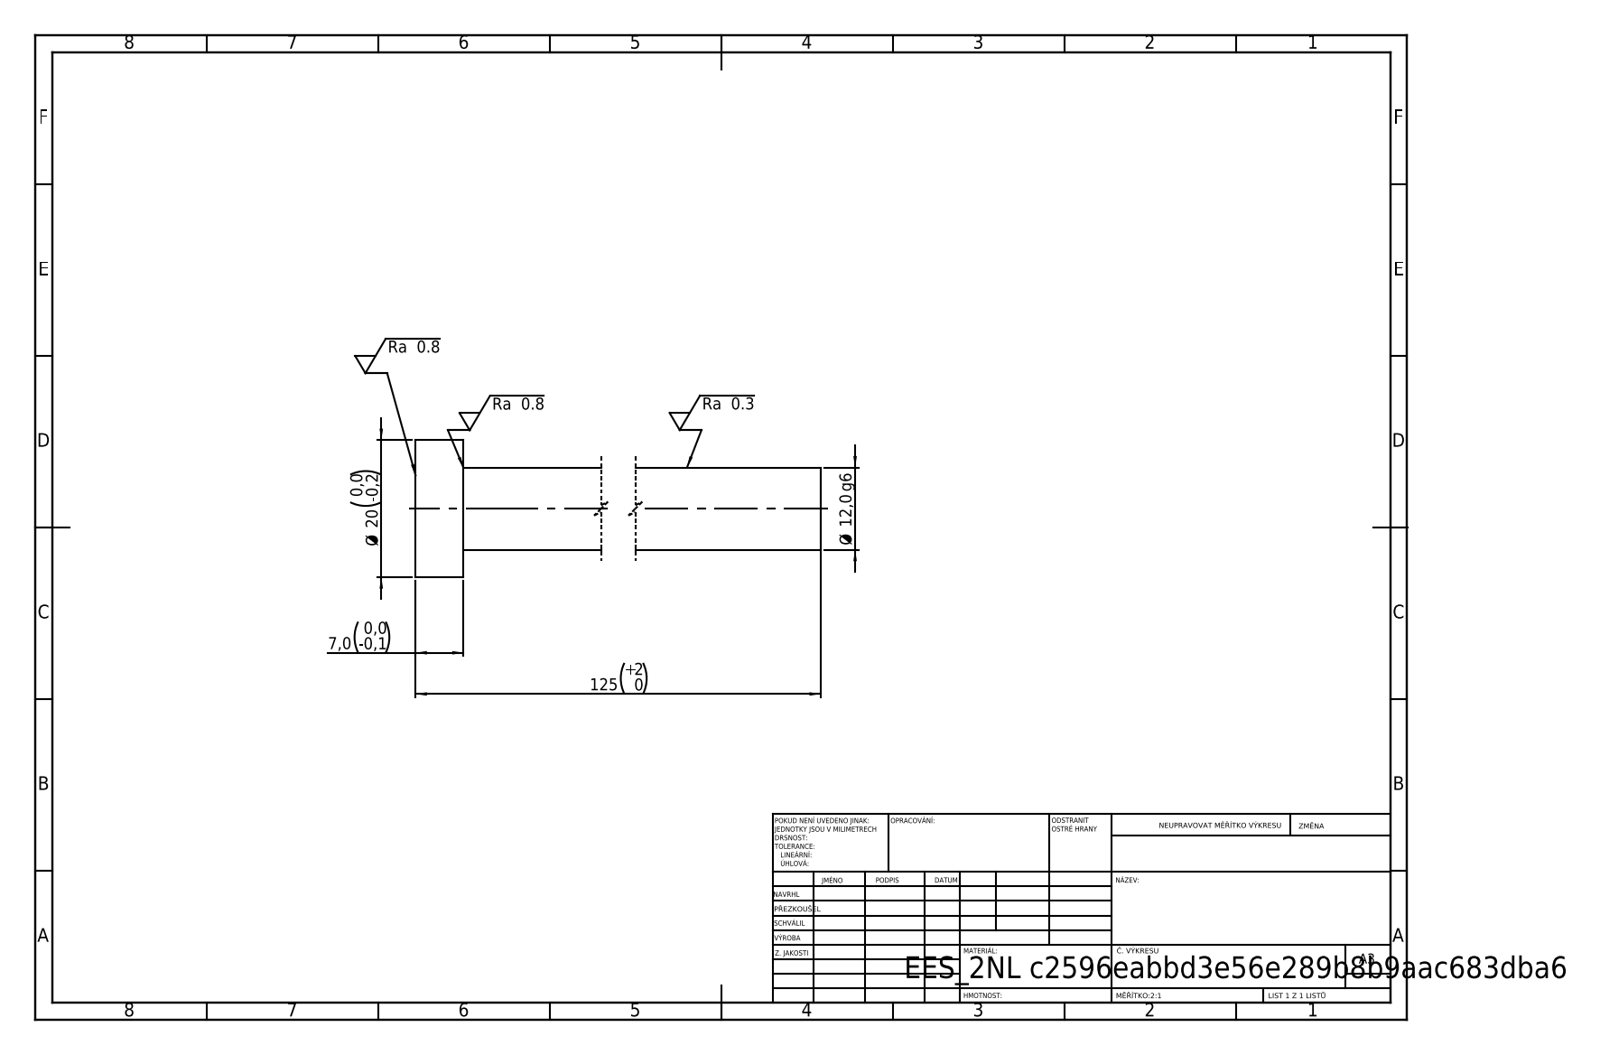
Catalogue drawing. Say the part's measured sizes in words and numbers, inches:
Its 3-D file was written by "SolidWorks 2019 (CONFIG_CONTROL_DESIGN)". It is 1 solid with 7 faces: 3 planar, 4 cylindrical and 0 other. Overall it measures 4.921 by 0.787 by 0.787 inches. Its volume is 0.949 cubic inches and its surface area 8.551 square inches. Round bosses or shafts: 1 of diameter 0.787, 1 of diameter 0.472. The main face-to-face distances are 0.276, 4.921, 4.646.
